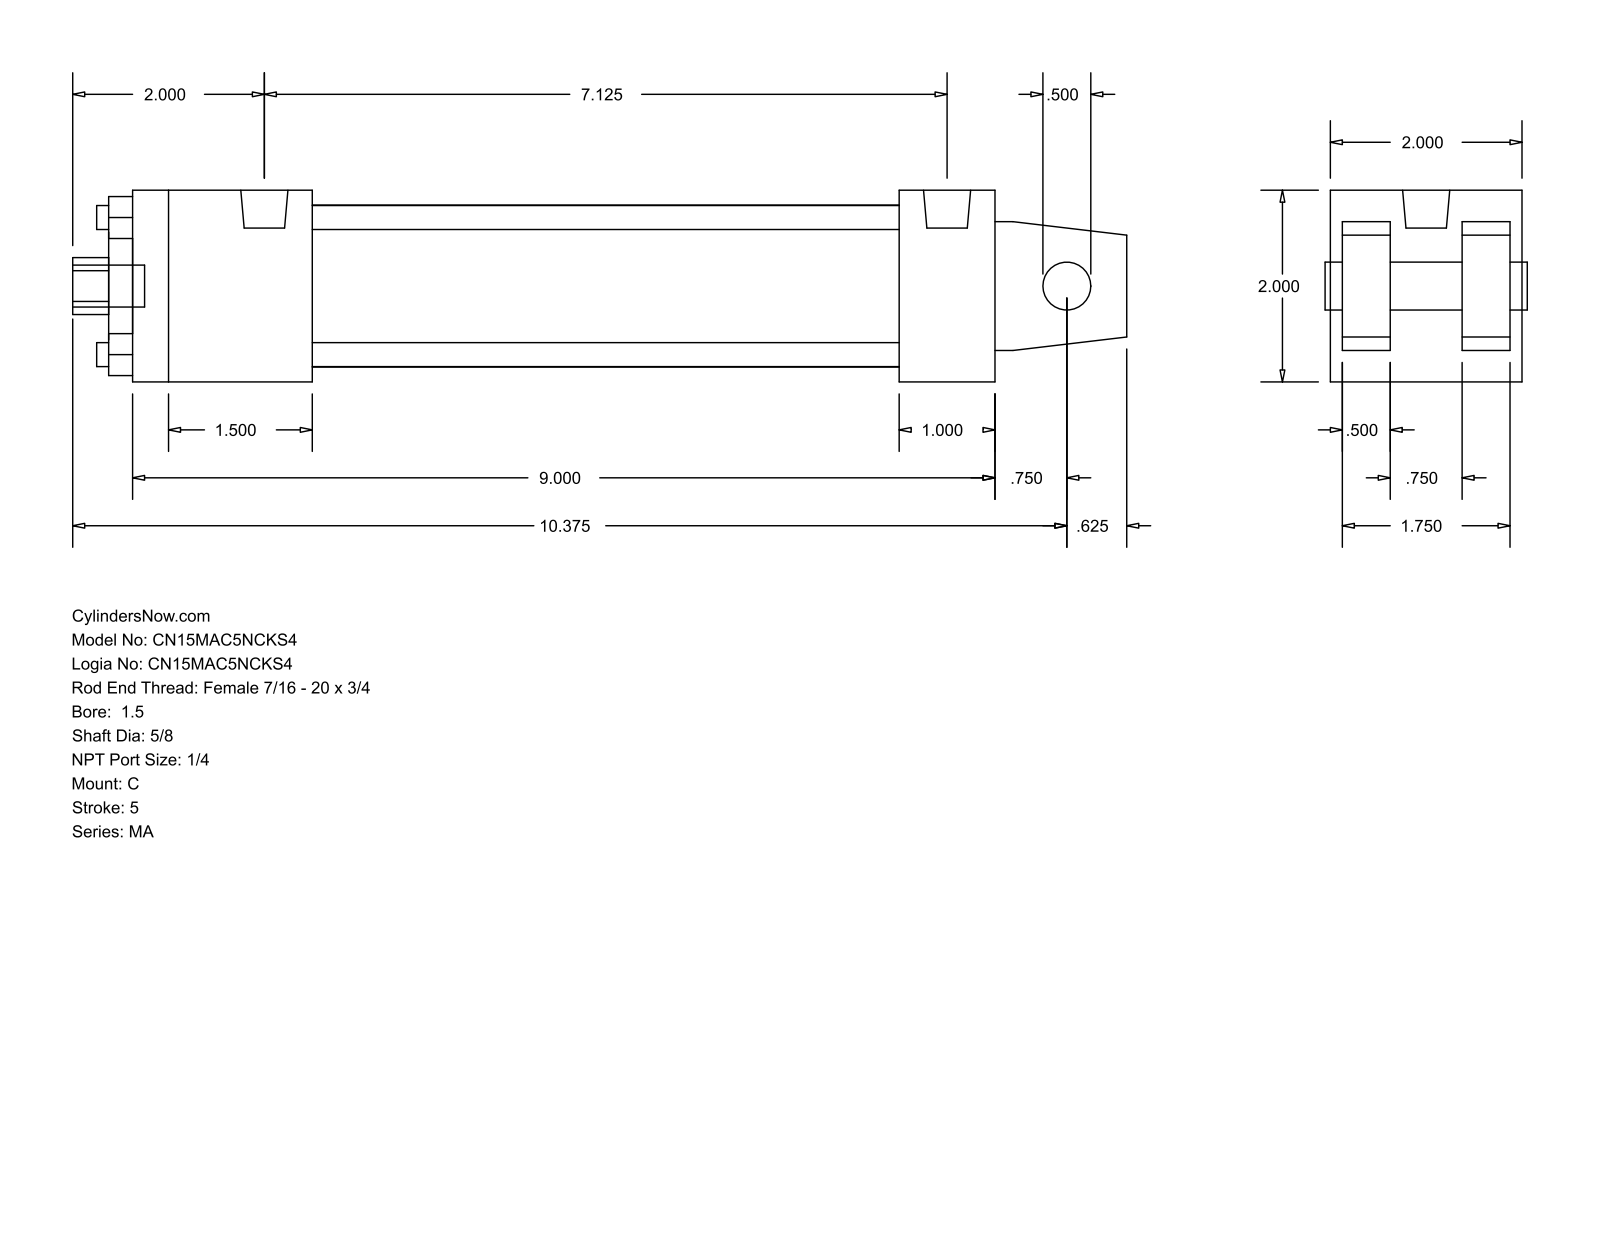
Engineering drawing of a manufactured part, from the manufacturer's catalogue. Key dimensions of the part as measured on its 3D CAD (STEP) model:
Part name (STEP PRODUCT): MA_C__0150_0.625
STEP written by: GSSL Pune (CONFIG_CONTROL_DESIGN)
Units: millimetres
Bodies: 0 solids, 103 faces (76 planar, 27 cylindrical, 0 other)
Overall size (bounding box): 279.4 × 50.8 × 50.8
Round holes (diameter × count): ⌀6.35 ×4, ⌀12.7 ×1, ⌀15.88 ×1, ⌀28.57 ×1, ⌀42.93 ×1
Round bosses / shafts (diameter × count): ⌀7.94 ×4, ⌀12.49 ×2, ⌀11.11 ×1
Partial cylindrical surfaces — rounded edges, fillets, slot ends (radius × count): R7.54 ×1
Main face-to-face distances: 50.8, 34.93, 12.7, 3.17, 15.87, 47.63, 31.76, 228.59, 203.19, 25.4
Hole centre spacings: 25.68, 36.32, 51.36
